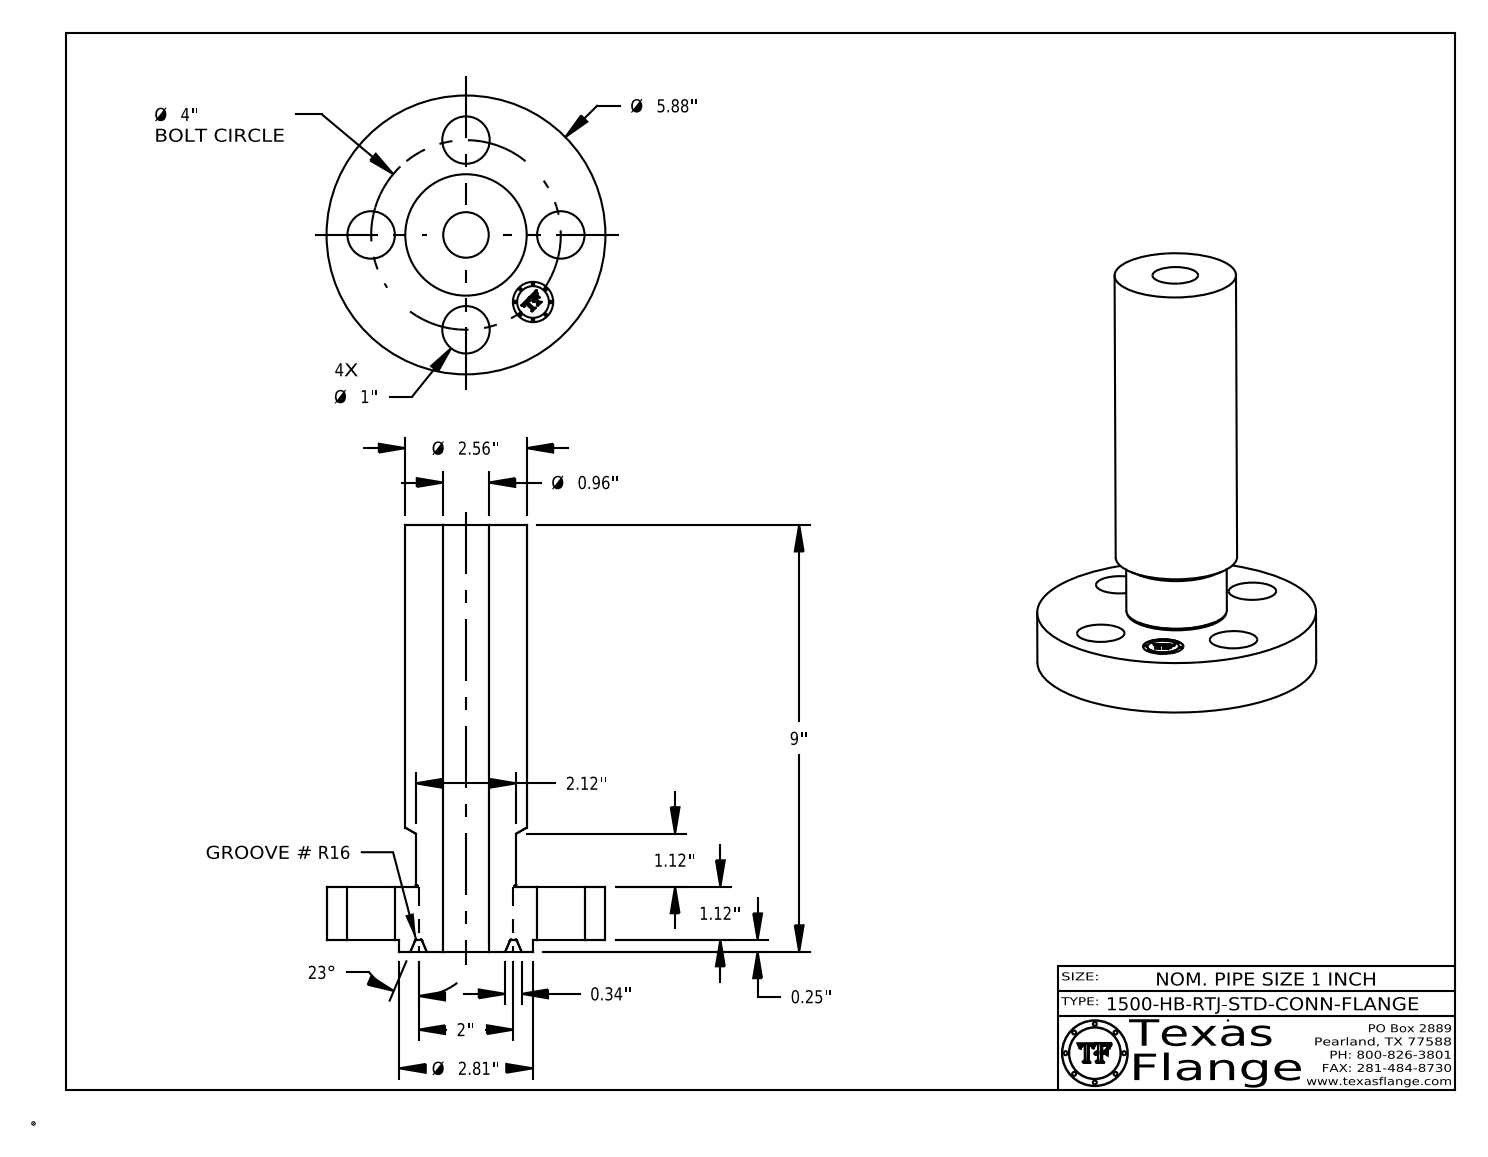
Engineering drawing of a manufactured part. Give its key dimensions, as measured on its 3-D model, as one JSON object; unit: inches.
{"part_name": "1-1500-HB-RTJ-STD-CONN-FLANGE", "step_written_by": "CATIA V5 STEP AP214 (AUTOMOTIVE_DESIGN)", "units": "inches", "bodies": {"solids": 1, "faces": 423, "planar": 371, "cylindrical": 38, "other": 14}, "overall_size": [9, 5.88, 5.88], "volume_in3": 58.91, "surface_area_in2": 175.3, "round_holes": [[1, 4], [0.85, 1], [0.96, 1]], "round_bosses_or_shafts": [[0.051, 8], [5.88, 1], [2.813, 1], [2.56, 1], [2.12, 1], [0.67, 1]], "face_to_face_distances": [1.12, 8.75, 7.63, 0.25, 1.37, 9, 1.365, 1.115, 7.635, 0.254], "hole_center_spacings": [2, 2.828, 1.531, 3.695, 4]}
